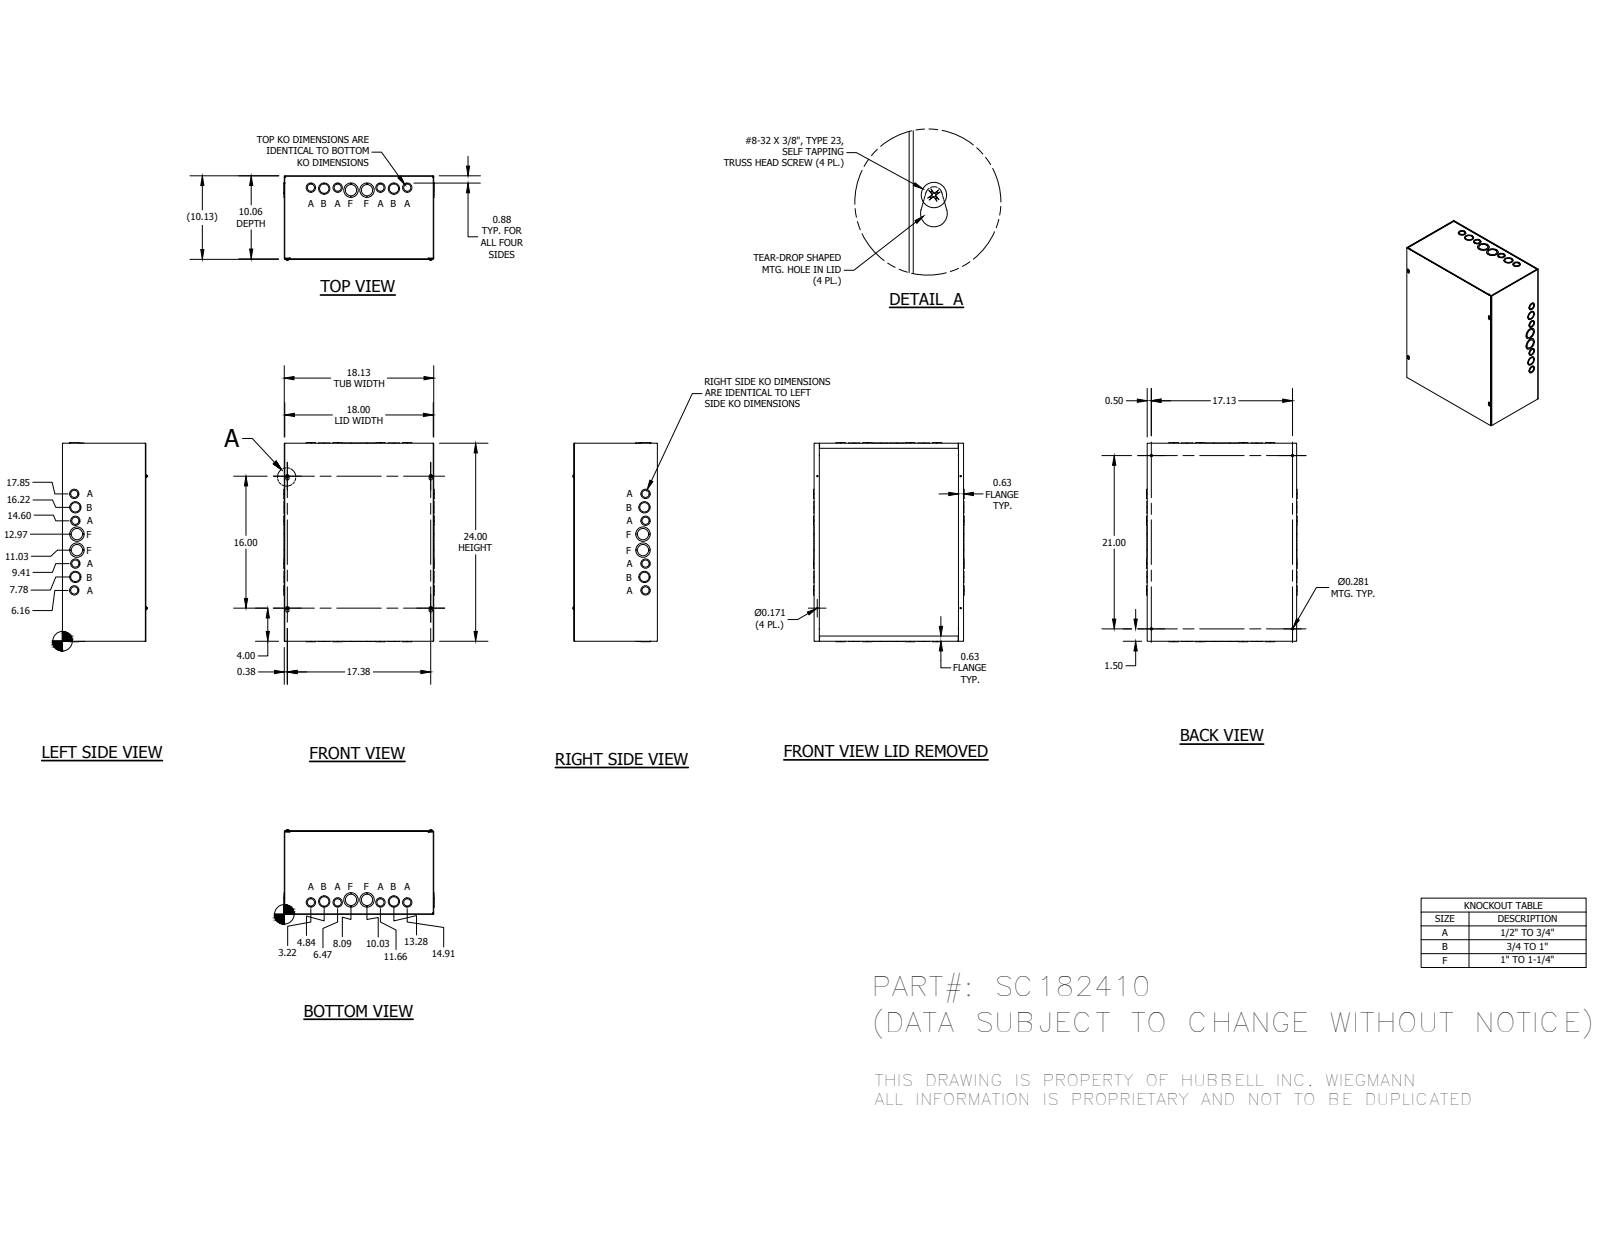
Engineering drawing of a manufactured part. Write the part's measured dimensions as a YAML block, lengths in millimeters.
part_name: "SC182410BLR; SC1810TB; SC1824LPA; 34056 (+1 more)"
step_written_by: "Autodesk Inventor 2014 (AUTOMOTIVE_DESIGN)"
units: millimeters
bodies: {solids: 37, faces: 1167, planar: 859, cylindrical: 240, other: 68}
overall_size: [612.77, 463.55, 259.72]
round_holes:
  - {diameter: 28.57, count: 14}
  - {diameter: 22.22, count: 10}
  - {diameter: 34.92, count: 8}
  - {diameter: 4.34, count: 4}
  - {diameter: 7.14, count: 4}
  - {diameter: 44.45, count: 4}
round_bosses_or_shafts:
  - {diameter: 9.75, count: 4}
  - {diameter: 4.17, count: 4}
partial_cylinders:
  - {radius: 0.79, count: 12}
  - {radius: 2.38, count: 12}
  - {radius: 3.17, count: 4}
  - {radius: 5.16, count: 4}
face_to_face_distances: [1.59, 255.59, 254, 458.79, 257.18, 608.01, 457.2, 460.38, 609.6, 606.42]
hole_center_spacings: [41.39, 41.4, 42.03, 63.58, 82.55, 82.69, 90.9, 124.07]
